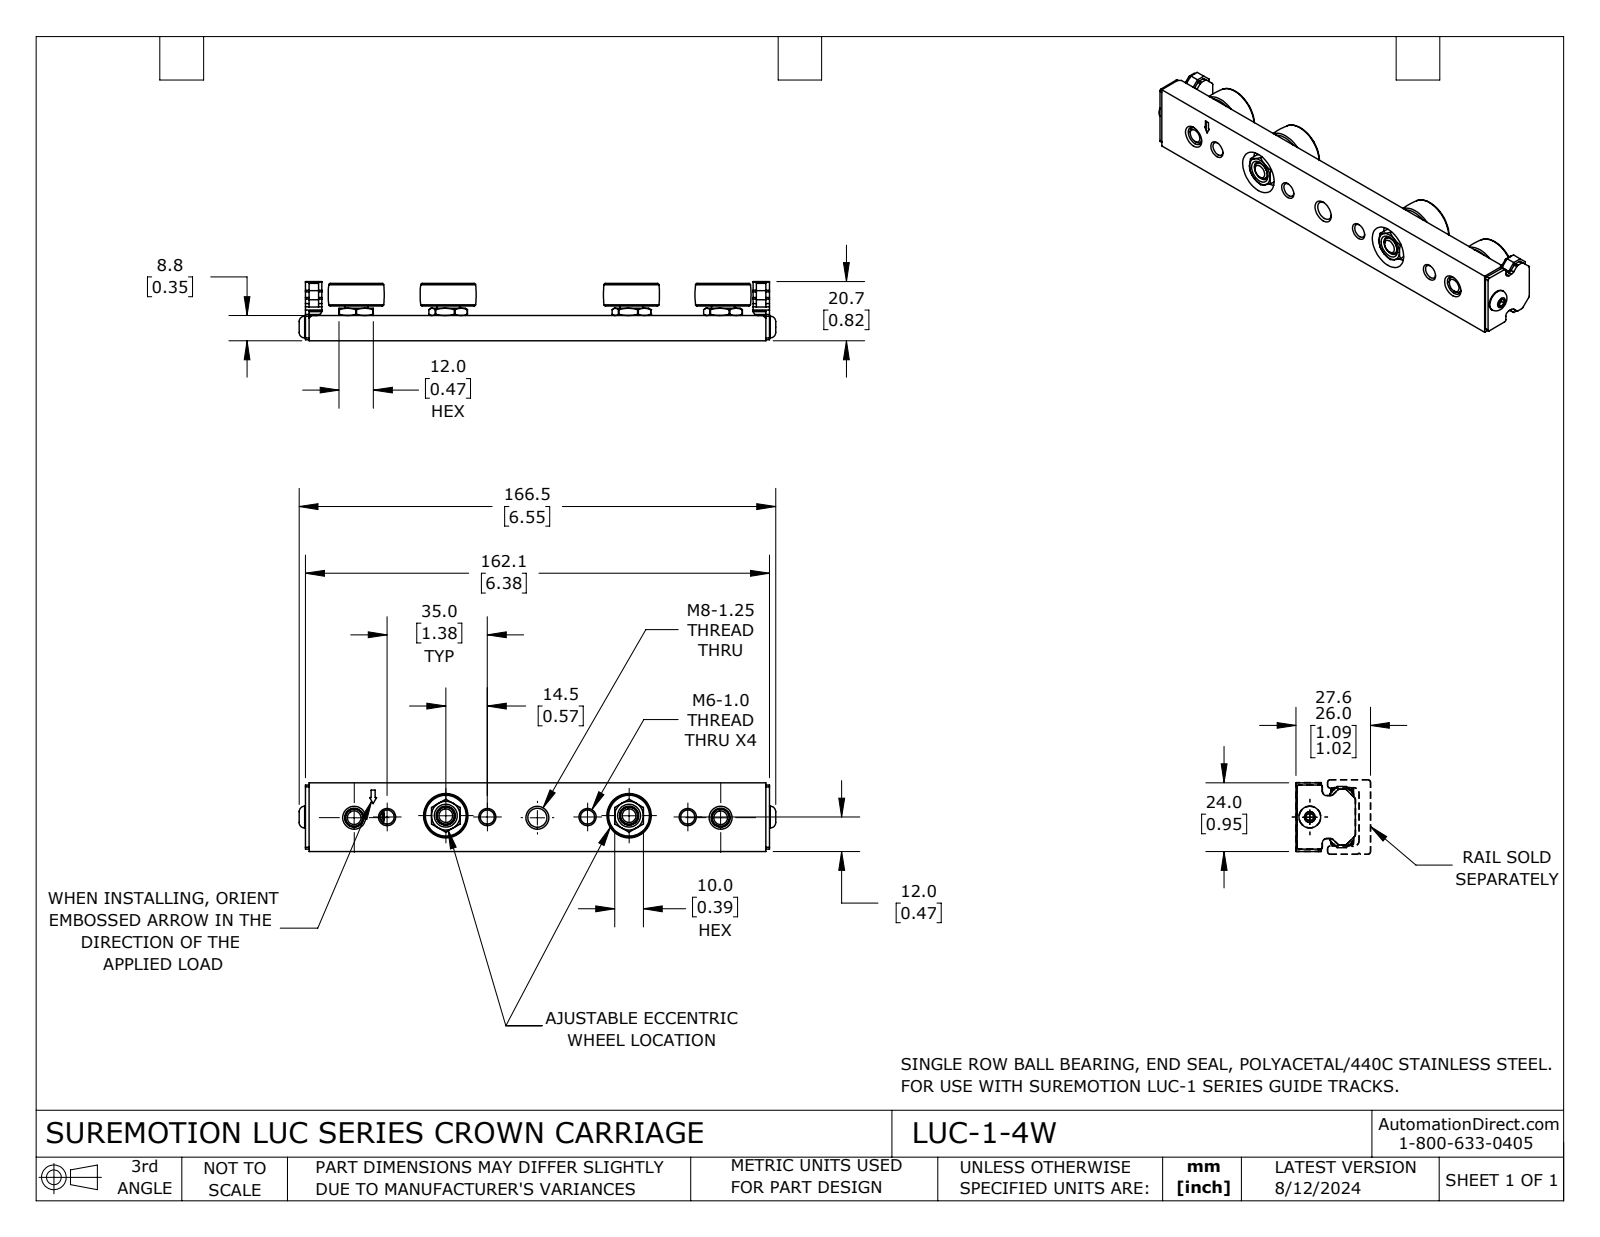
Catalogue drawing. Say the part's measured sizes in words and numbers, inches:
The part is named "LUC-1-4W". Its 3-D file was written by "SolidWorks 2023 (CONFIG_CONTROL_DESIGN)". It is 9 solids with 594 faces: 216 planar, 180 cylindrical and 198 other. Overall it measures 6.553 by 0.945 by 0.816 inches. Its volume is 2.678 cubic inches and its surface area 34.44 square inches. Round holes: 4 of diameter 0.194, 4 of diameter 0.262, 4 of diameter 0.472, 2 of diameter 0.25, 2 of diameter 0.61, 1 of diameter 0.128, 1 of diameter 0.262. Round bosses or shafts: 4 of diameter 0.315, 4 of diameter 0.248, 4 of diameter 0.236, 4 of diameter 0.173, 2 of diameter 0.561, 1 of diameter 0.299, 1 of diameter 0.157. Partial cylindrical surfaces (rounded edges, fillets, slot ends): 12 of radius 0.015, 6 of radius 0.033, 4 of radius 0.025, 4 of radius 0.063, 4 of radius 0.269, 2 of radius 0.07. The main face-to-face distances are 0.347, 0.945, 0.052, 0.258, 0.05, 6.33, 0.132, 0.479, 0.31, 0.442. The hole center spacings are 1.378, 0.033, 0.571, 0.807, 1.227, 1.259, 1.949, 2.52.
